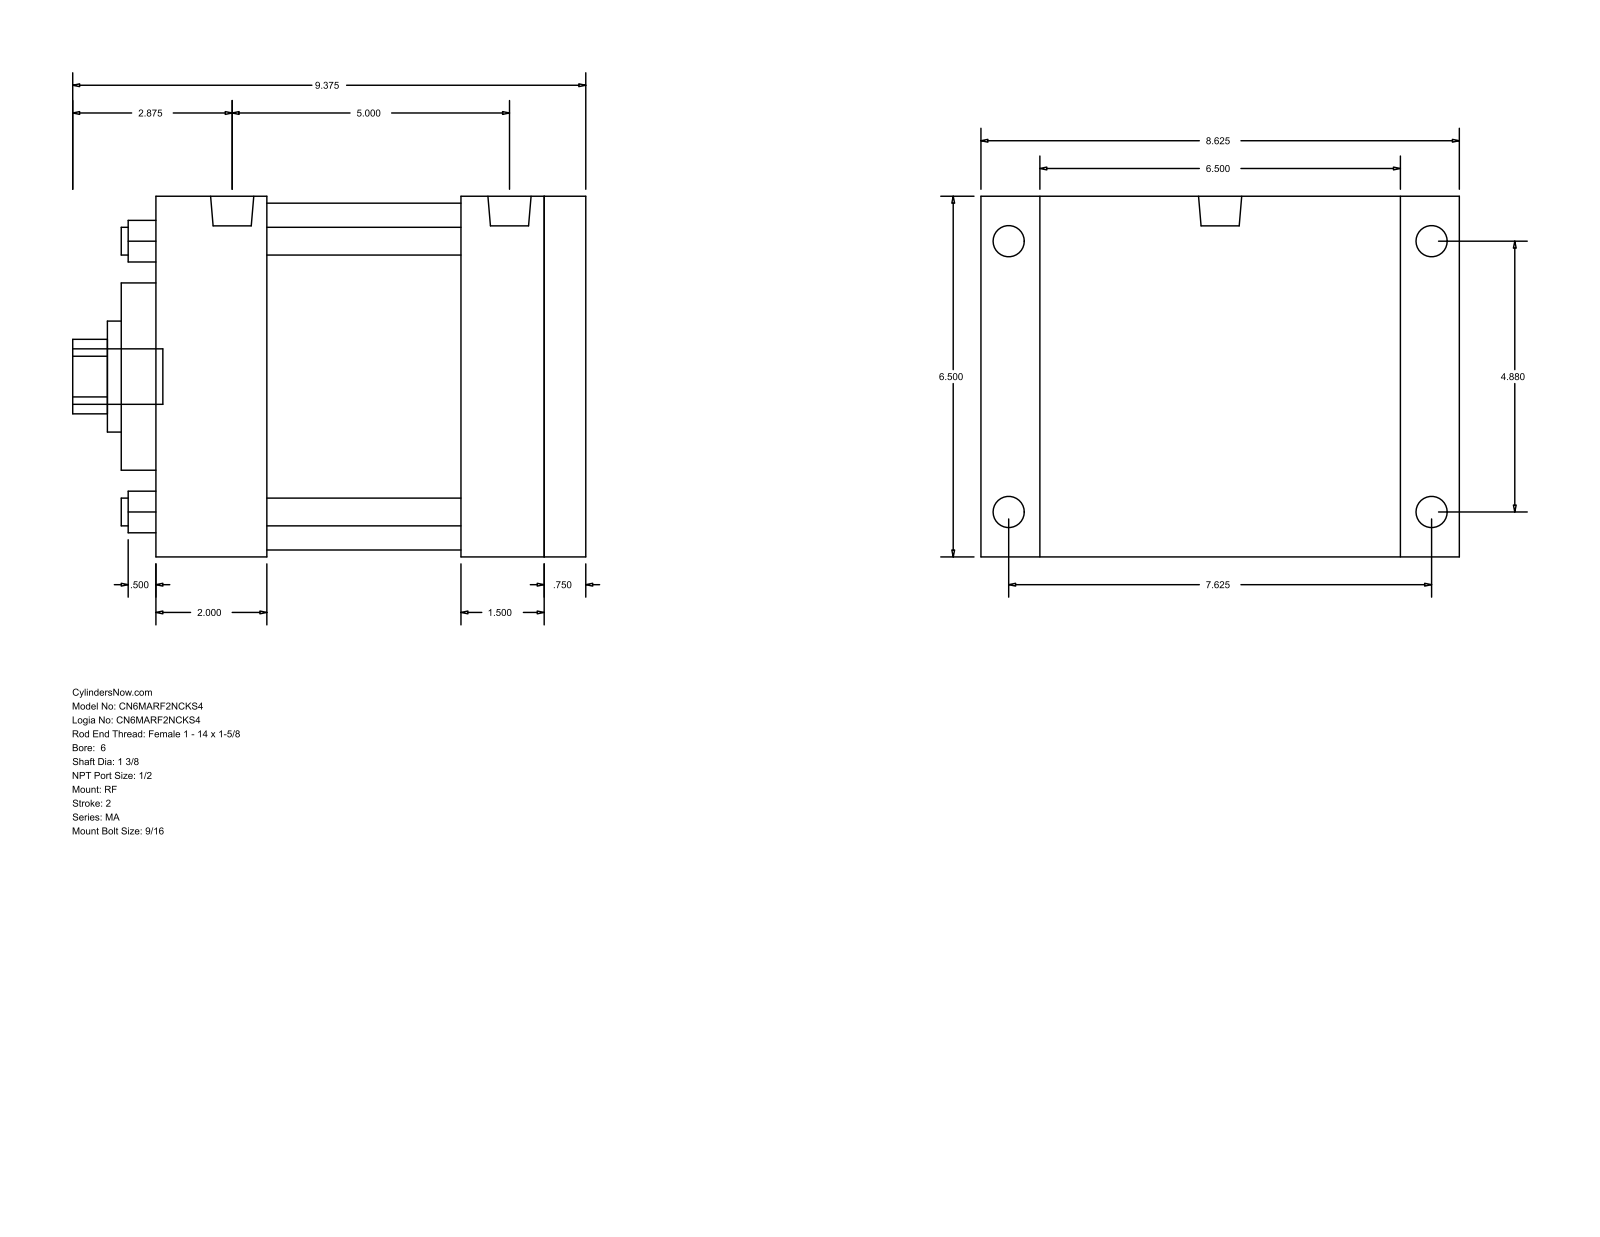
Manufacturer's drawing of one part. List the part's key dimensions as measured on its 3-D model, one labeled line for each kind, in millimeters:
Part name (STEP PRODUCT): MA_RF__0600_1.375
STEP written by: GSSL Pune (CONFIG_CONTROL_DESIGN)
Units: millimetres
Bodies: 0 solids, 94 faces (65 planar, 29 cylindrical, 0 other)
Overall size (bounding box): 238.12 × 219.07 × 165.1
Round holes (diameter × count): ⌀12.7 ×4, ⌀34.92 ×1, ⌀50.8 ×1, ⌀85.72 ×1, ⌀158.75 ×1
Round bosses / shafts (diameter × count): ⌀17.46 ×4, ⌀14.29 ×4, ⌀19.77 ×2, ⌀25.4 ×1
Partial cylindrical surfaces — rounded edges, fillets, slot ends (radius × count): R17.06 ×1
Main face-to-face distances: 165.1, 200.02, 19.05, 180.97, 38.1, 50.8, 130.17, 149.22, 142.87, 92.07
Hole centre spacings: 87.65, 123.96, 175.31
